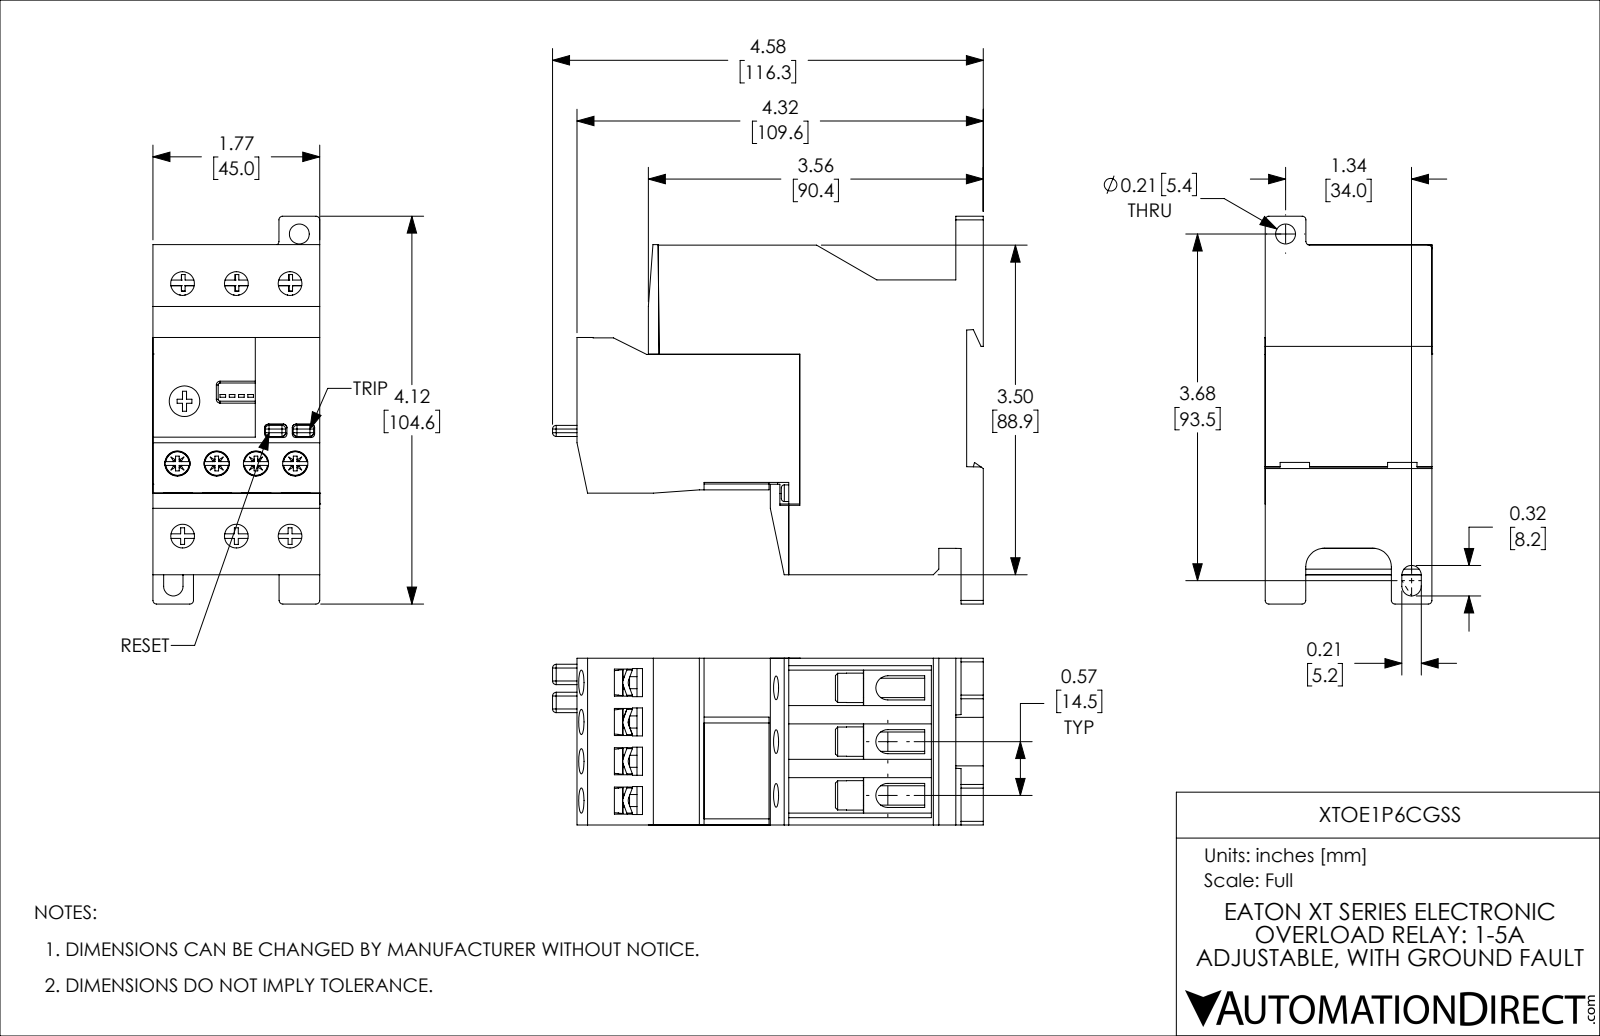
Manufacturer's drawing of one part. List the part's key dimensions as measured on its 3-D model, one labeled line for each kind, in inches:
Part name (STEP PRODUCT): XTOE1P6CGSS
STEP written by: SolidWorks 2018 (AUTOMOTIVE_DESIGN)
Units: inches
Bodies: 42 solids, 1296 faces (854 planar, 281 cylindrical, 161 other)
Overall size (bounding box): 4.577 × 4.118 × 1.772
Volume: 17.85 in³ · Surface area: 117.6 in²
Round holes (diameter × count): ⌀0.252 ×6, ⌀0.14 ×5, ⌀0.268 ×4, ⌀0.313 ×3, ⌀0.086 ×2, ⌀0.126 ×2, ⌀0.212 ×1
Round bosses / shafts (diameter × count): ⌀0.134 ×4, ⌀0.128 ×4, ⌀0.11 ×4, ⌀0.098 ×4, ⌀0.315 ×3, ⌀0.177 ×2, ⌀0.326 ×1
Partial cylindrical surfaces — rounded edges, fillets, slot ends (radius × count): R0.02 ×64, R0.012 ×24, R0.039 ×22, R0.079 ×10, R0.128 ×6, R0.031 ×4, R0.016 ×3, R0.062 ×2
Main face-to-face distances: 1.772, 0.571, 0.074, 0.429, 0.177, 1.772, 1.771, 1.142, 1.949, 0.644
Hole centre spacings: 0.417, 0.835, 0.417, 0.418, 0.773, 1.911, 1.922, 2.011
